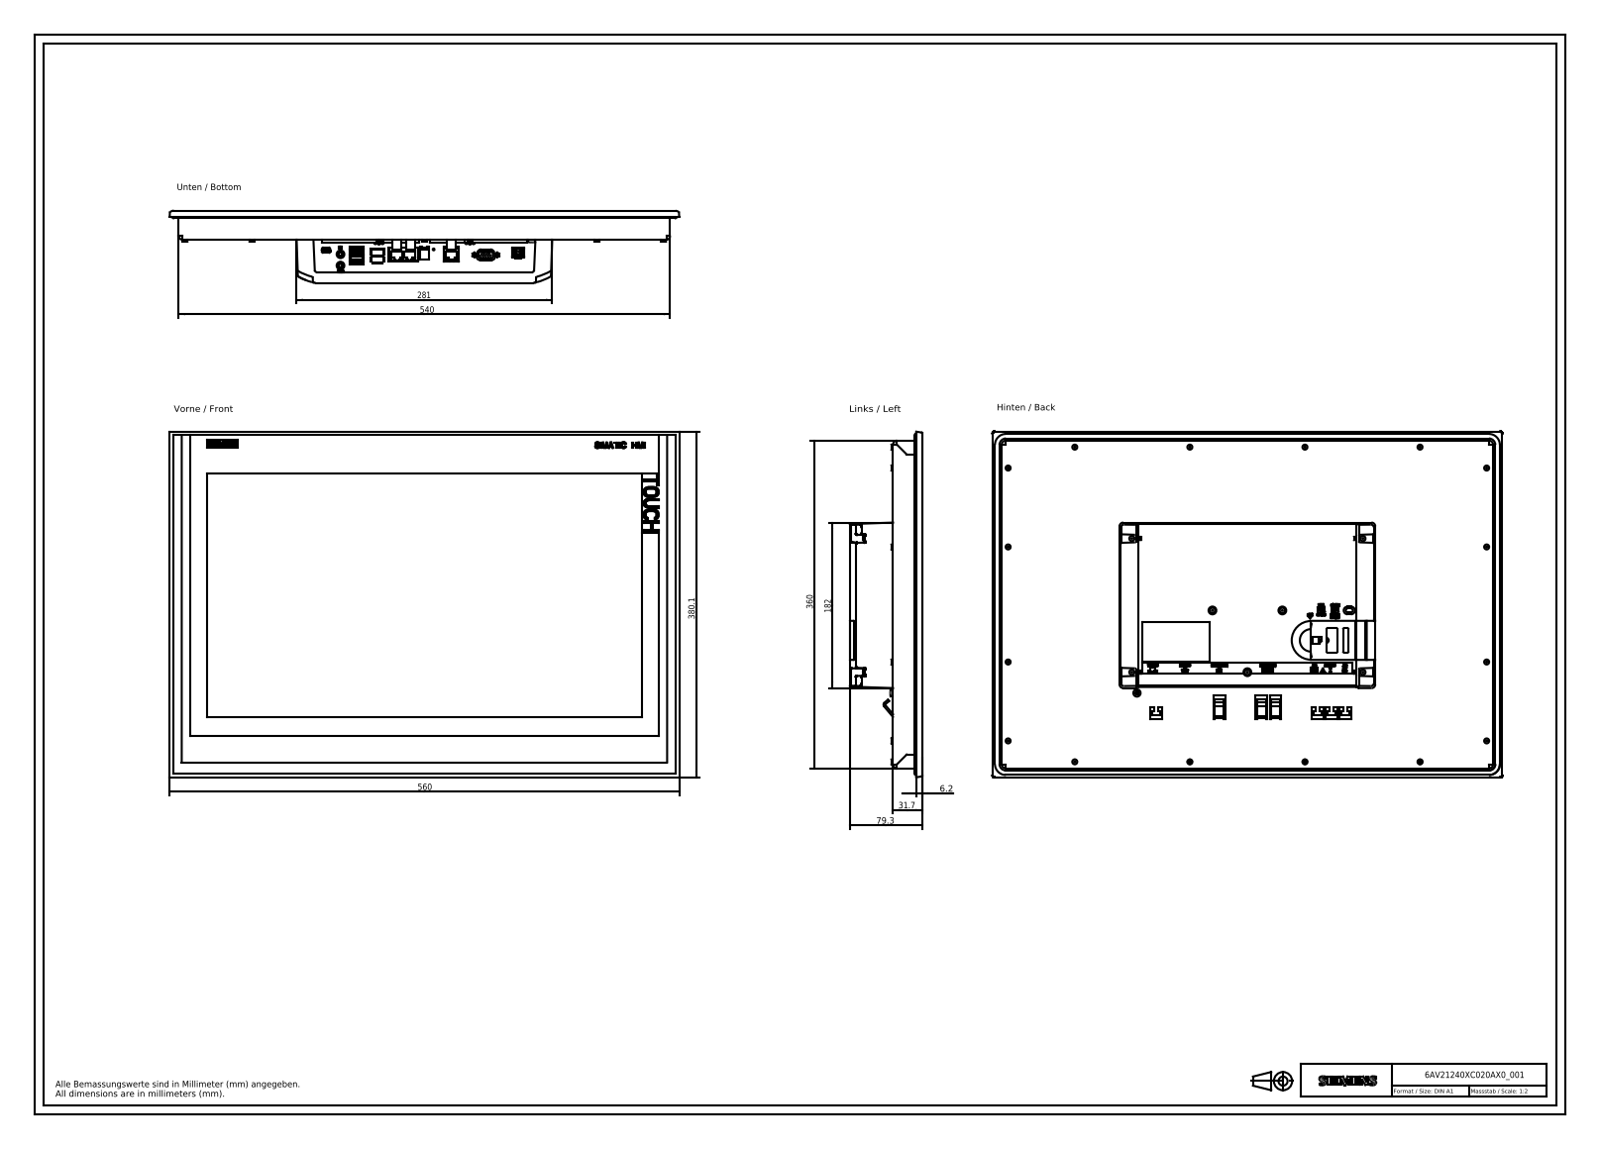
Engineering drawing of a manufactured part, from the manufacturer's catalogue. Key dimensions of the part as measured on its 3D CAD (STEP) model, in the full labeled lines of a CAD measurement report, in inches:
Part name (STEP PRODUCT): A5E30321192A_001; A5E30983812A_001; A5E30983808A_001; A5E30983805A_001 (+1 more)
STEP written by: SIEMENS PLM Software NX 7.5 (AUTOMOTIVE_DESIGN)
Units: inches
Bodies: 246 solids, 2773 faces (2306 planar, 220 cylindrical, 247 other)
Overall size (bounding box): 22.047 × 14.963 × 3.126
Volume: 519.2 in³ · Surface area: 1 075 in²
Round holes (diameter × count): ⌀0.031 ×9, ⌀0.316 ×3, ⌀0.071 ×2, ⌀0.094 ×2, ⌀0.112 ×2, ⌀0.15 ×2, ⌀0.335 ×2
Round bosses / shafts (diameter × count): ⌀0.236 ×8, ⌀0.276 ×2, ⌀0.12 ×2, ⌀0.118 ×2, ⌀0.079 ×2, ⌀0.315 ×1
Partial cylindrical surfaces — rounded edges, fillets, slot ends (radius × count): R0.033 ×48, R0.05 ×8, R0.039 ×4, R0.073 ×4, R0.156 ×4, R0.276 ×4, R0.473 ×4, R2.362 ×4
Main face-to-face distances: 1.22, 0.374, 1.594, 0.335, 0.039, 1.555, 1.5, 1.539, 1.874, 3.094
Hole centre spacings: 0.114, 0.108, 0.19, 0.216, 0.288, 0.324, 0.391, 0.492
